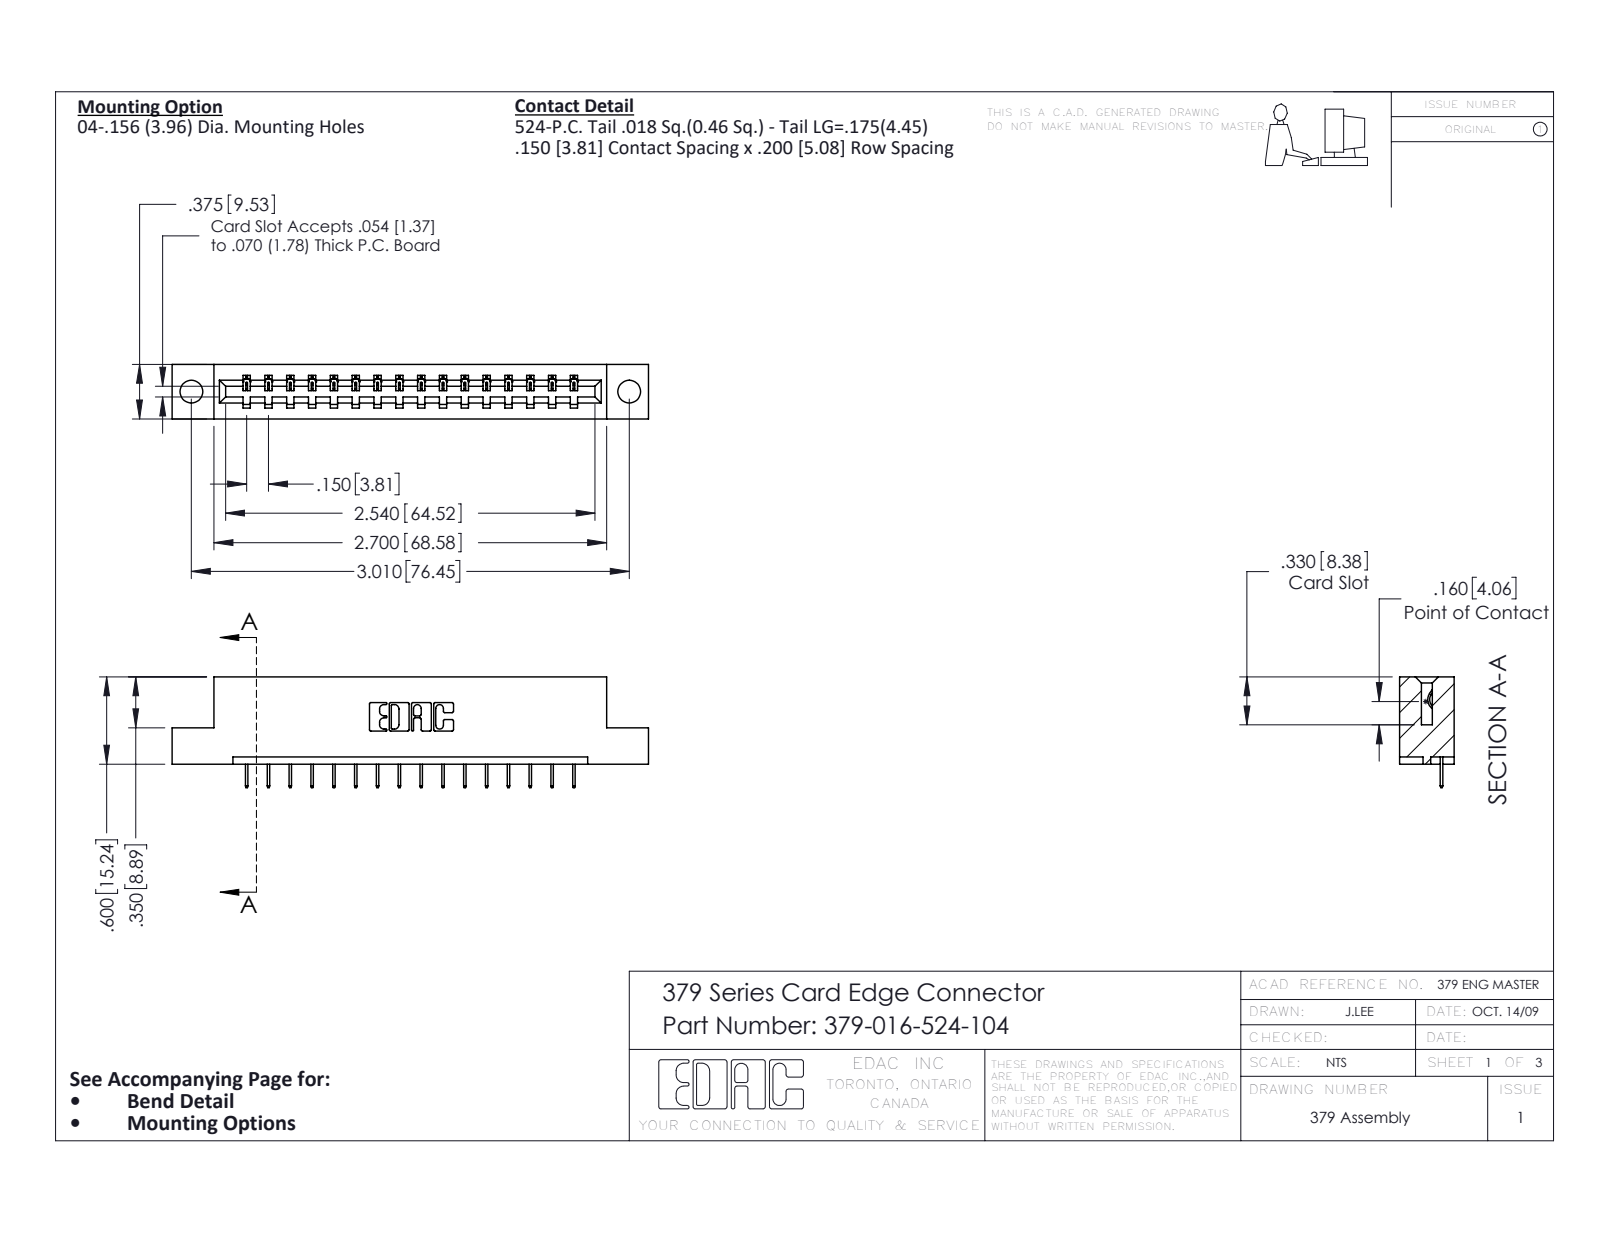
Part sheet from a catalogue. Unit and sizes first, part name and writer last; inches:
Units: inches
Overall size (bounding box): 3.275 × 0.762 × 0.375
Round holes (diameter × count): ⌀0.156 ×2
Partial cylindrical surfaces — rounded edges, fillets, slot ends (radius × count): R0.006 ×32, R0.01 ×22, R0.007 ×6, R0.031 ×6, R0.026 ×3, R0.014 ×1, R0.022 ×1, R0.024 ×1
Main face-to-face distances: 0.3, 0.375, 0.075, 0.6, 0.15, 0.225, 0.45, 0.75, 0.2, 0.9
Hole centre spacings: 3.01
Volume: 0.505 in³ · Surface area: 12.26 in²
Bodies: 17 solids, 1106 faces (838 planar, 268 cylindrical, 0 other)
Part name (STEP PRODUCT): 379 Part_Flush - .156 Dia - TH; 345-292-001_345-293-124; 379-016-524-104
STEP written by: SolidWorks 2020 (CONFIG_CONTROL_DESIGN)
